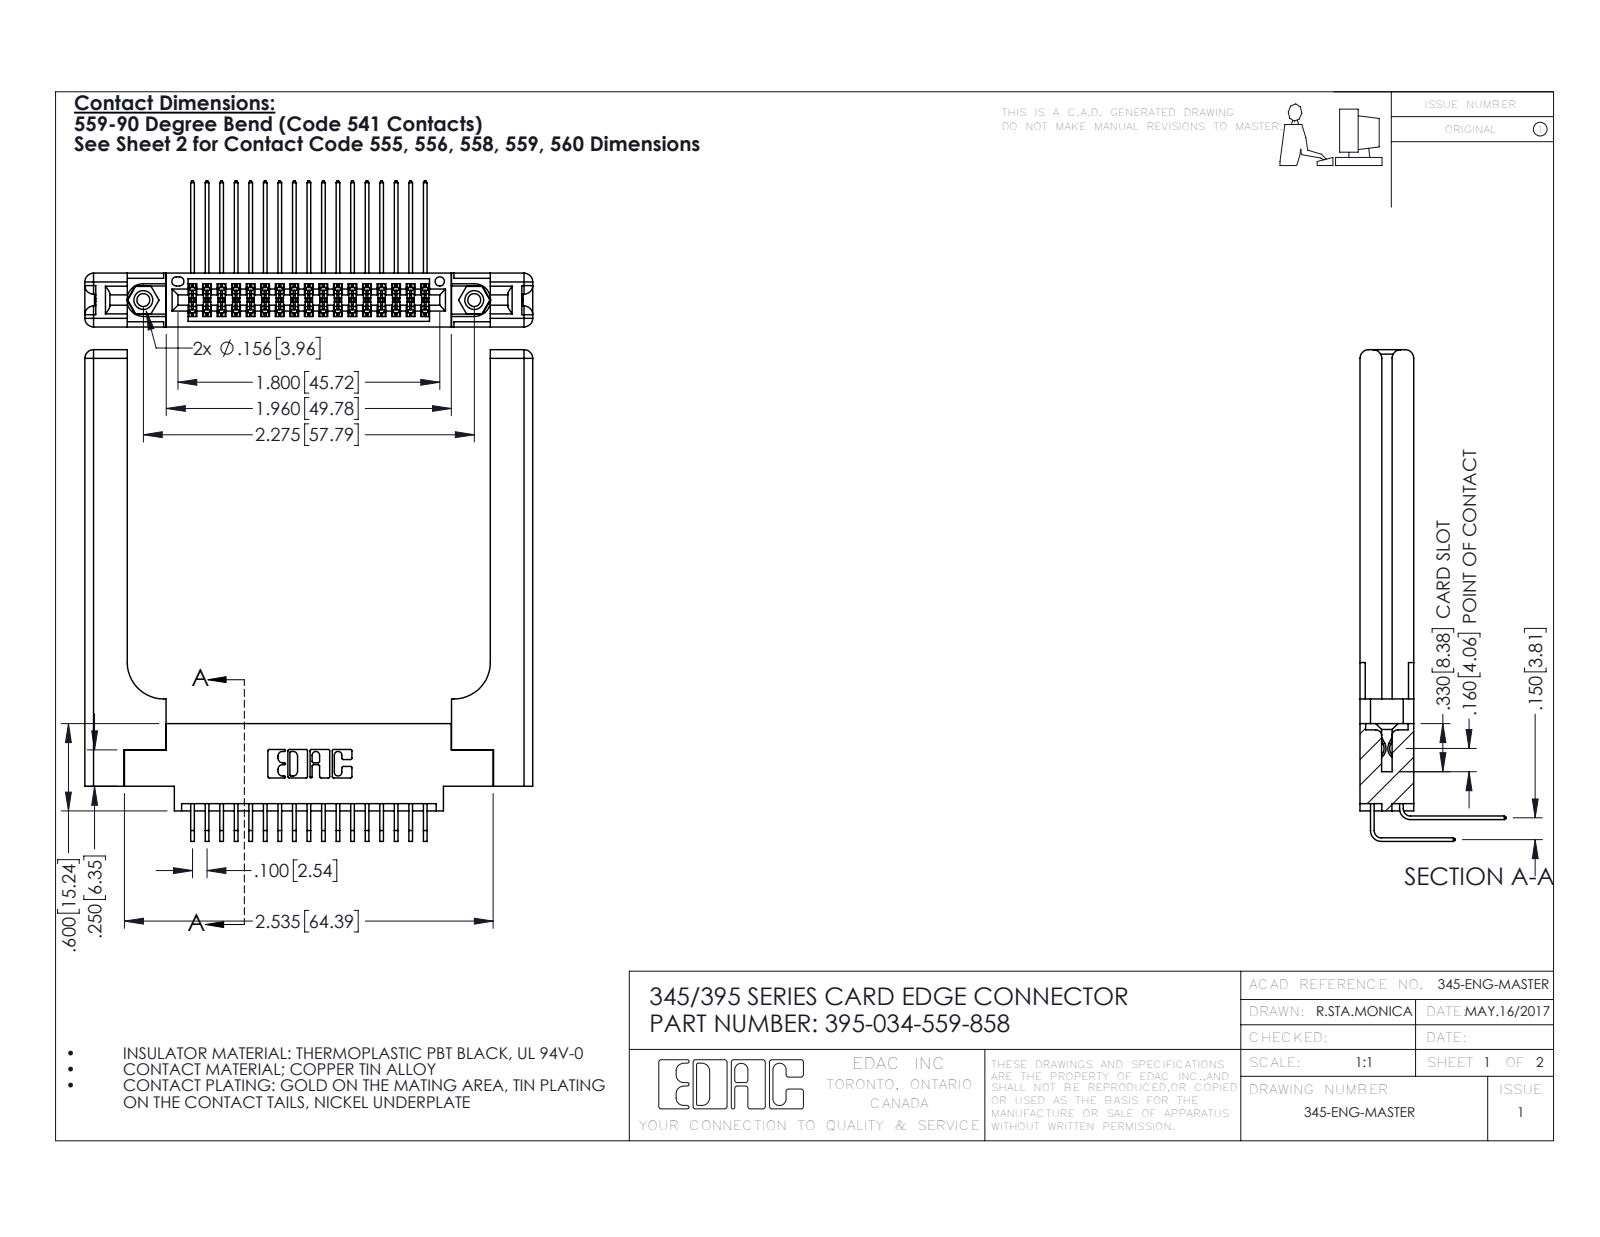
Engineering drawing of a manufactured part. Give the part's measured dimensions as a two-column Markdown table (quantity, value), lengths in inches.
| quantity | value |
| --- | --- |
| part name | 345-292-001_558 559 Tail - 1; 345-292-001_559 Tail - 2; 345 Part_0.170 Offset - 0.156 Dia-TH; 345-250-001_345-250-001-102 (+2 more) |
| STEP written by | SolidWorks 2016 (CONFIG_CONTROL_DESIGN) |
| units | inches |
| bodies | 39 solids, 2154 faces (1422 planar, 672 cylindrical, 60 other) |
| overall size | 3.379 × 3.079 × 1.005 |
| volume | 0.972 in³ |
| surface area | 25.81 in² |
| round holes (diameter × count) | 0.089 × 2, 0.125 × 2, 0.156 × 2, 0.064 × 1 |
| round bosses / shafts (diameter × count) | 0.155 × 2 |
| partial cylindrical surfaces (radius × count) | 0.006 × 52, 0.01 × 22, 0.06 × 16, 0.007 × 6, 0.031 × 6, 0.026 × 3, 0.014 × 2, 0.019 × 2 |
| main face-to-face distances | 0.37, 0.072, 0.298, 0.148, 0.15, 0.077, 0.22, 0.225, 0.098, 0.272 |
| hole center spacings | 0.27, 2.041, 2.275 |
